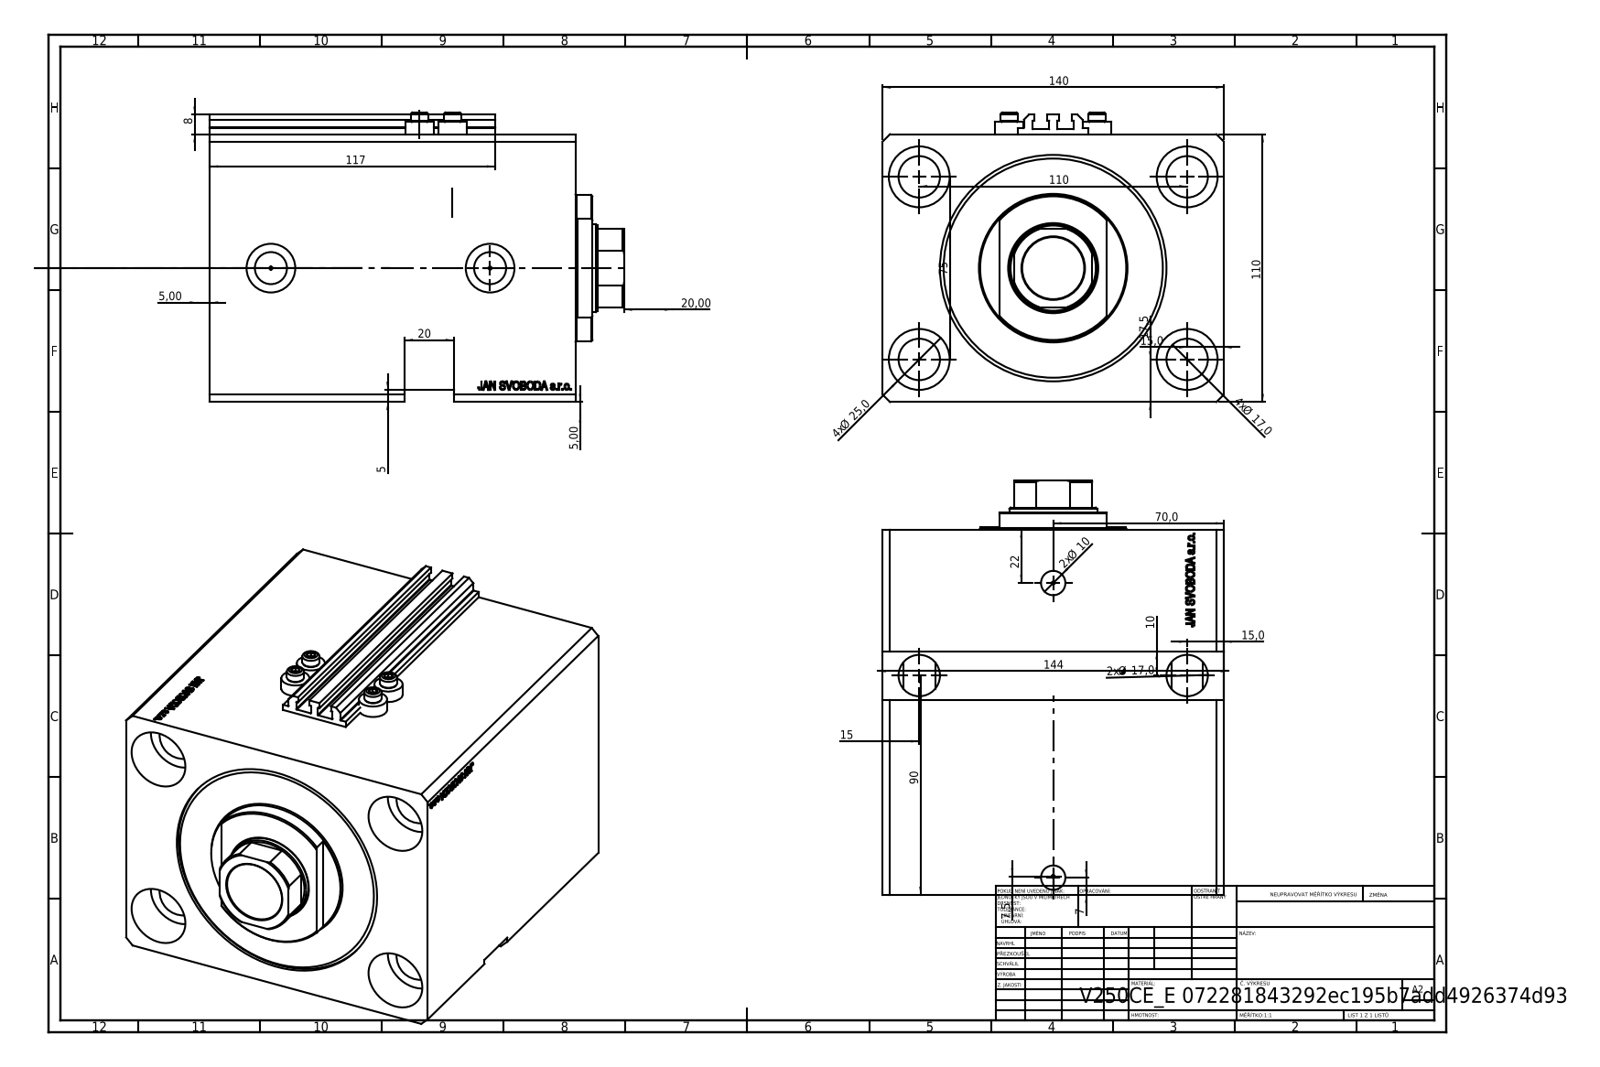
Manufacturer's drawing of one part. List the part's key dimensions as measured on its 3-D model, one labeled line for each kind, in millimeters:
Part name (STEP PRODUCT): ALLEN BOLT V250CE; V250CE_E_Body; V250CE_C_VCP; V250CE_VC_E
STEP written by: SolidWorks 2019 (CONFIG_CONTROL_DESIGN)
Units: millimetres
Bodies: 8 solids, 1112 faces (548 planar, 126 cylindrical, 438 other)
Overall size (bounding box): 170 × 140 × 119
Volume: 1 909 000 mm³ · Surface area: 256 399 mm²
Round holes (diameter × count): ⌀17 ×6, ⌀1.25 ×4, ⌀4 ×4, ⌀25 ×4, ⌀10 ×2, ⌀13.16 ×2, ⌀20 ×2, ⌀25.5 ×1, ⌀36 ×1, ⌀80 ×1, ⌀93 ×1
Round bosses / shafts (diameter × count): ⌀11.6 ×4, ⌀7 ×4, ⌀60 ×1
Partial cylindrical surfaces — rounded edges, fillets, slot ends (radius × count): R0.2 ×10, R17.5 ×1
Main face-to-face distances: 110, 140, 150, 25, 125, 33, 92, 117, 50, 83
Hole centre spacings: 66.57, 110, 13.6, 33.62, 36, 37.22, 38.23, 38.48
